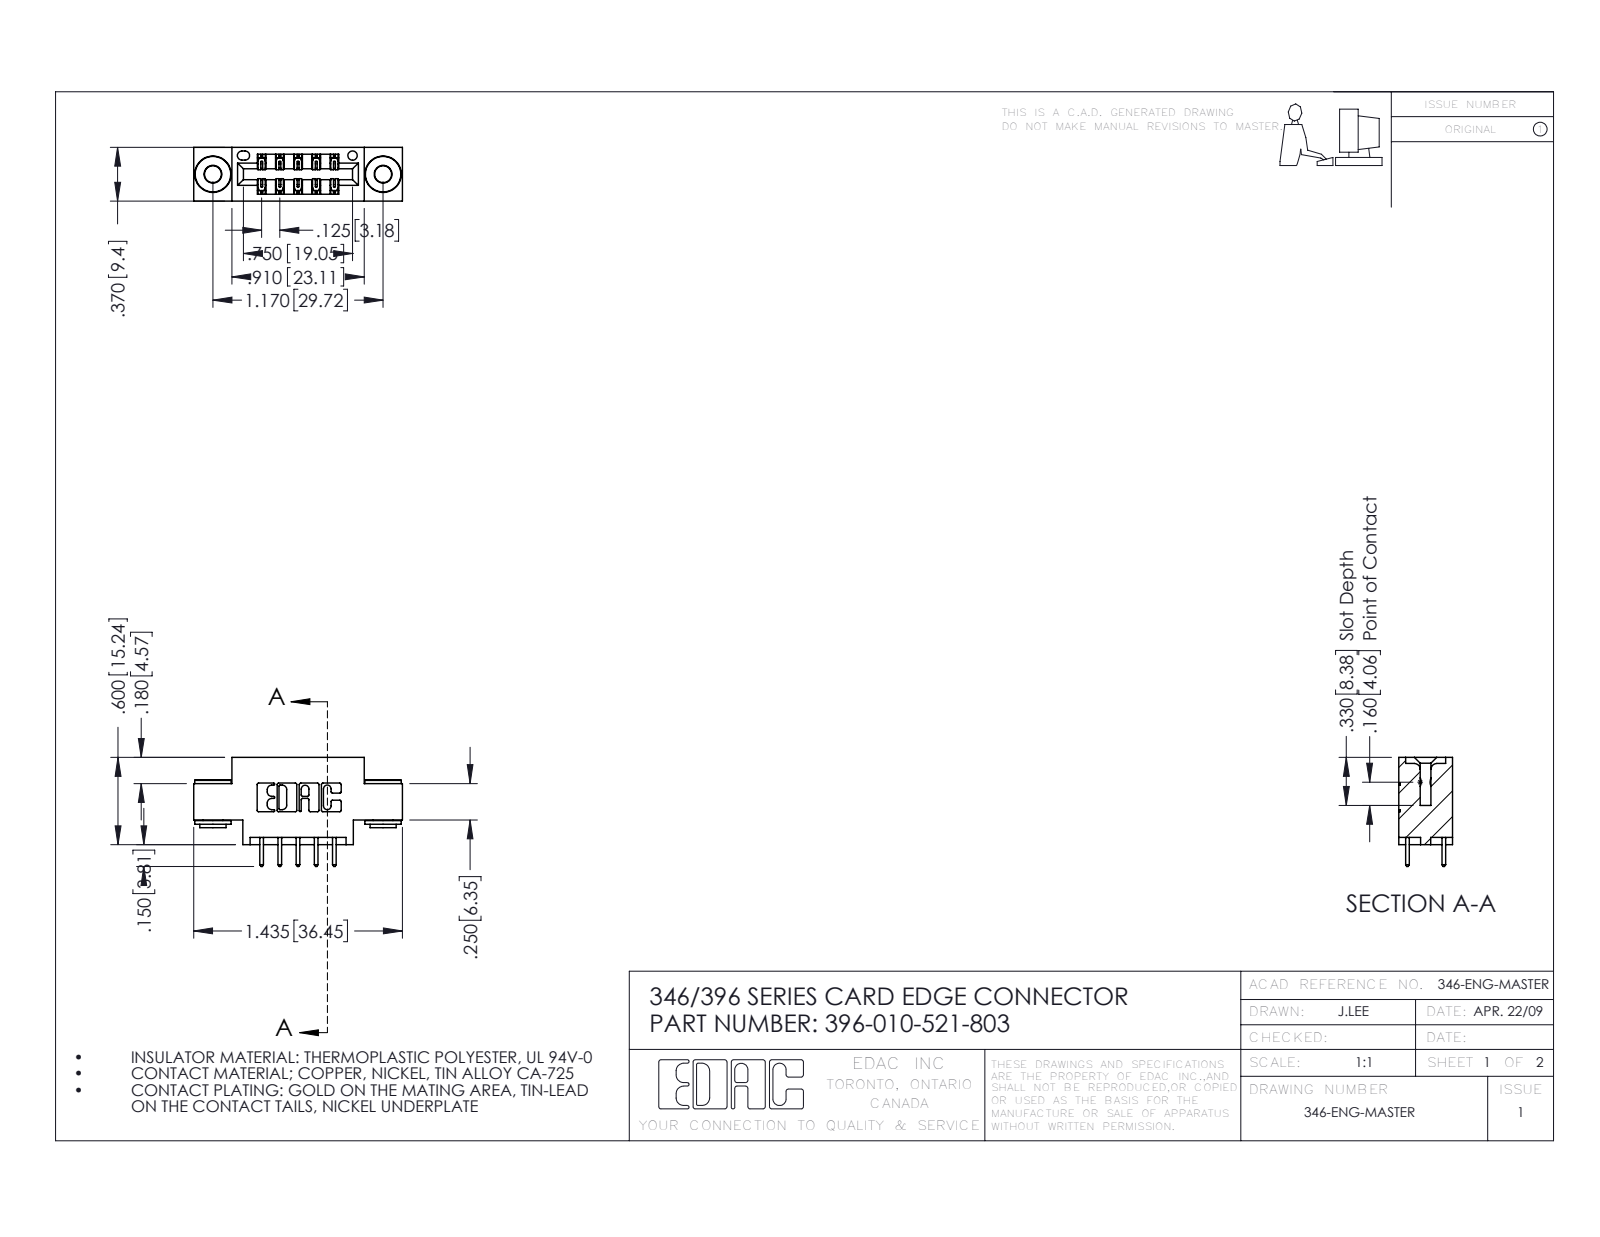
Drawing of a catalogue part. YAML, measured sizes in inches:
part_name: "345-292-001_345-293-121; 345-250-002_345-250-002-102; 346 Part_0.170 Offset - 0.156 Dia-TH; 396-010-521-803"
step_written_by: "SolidWorks 2016 (CONFIG_CONTROL_DESIGN)"
units: inches
bodies: {solids: 13, faces: 684, planar: 440, cylindrical: 236, other: 8}
overall_size: [1.435, 0.75, 0.37]
volume: 0.191
surface_area: 6.33
round_holes:
  - {diameter: 0.116, count: 2}
  - {diameter: 0.156, count: 2}
  - {diameter: 0.064, count: 1}
round_bosses_or_shafts:
  - {diameter: 0.25, count: 2}
  - {diameter: 0.18, count: 2}
  - {diameter: 0.136, count: 2}
partial_cylinders:
  - {radius: 0.01, count: 22}
  - {radius: 0.006, count: 15}
  - {radius: 0.01, count: 10}
  - {radius: 0.007, count: 6}
  - {radius: 0.031, count: 6}
  - {radius: 0.026, count: 3}
  - {radius: 0.014, count: 2}
  - {radius: 0.022, count: 2}
face_to_face_distances: [0.25, 0.37, 0.048, 0.322, 0.025, 0.275, 0.072, 0.298, 0.148, 0.222]
hole_center_spacings: [0.246, 0.969, 1.17]
